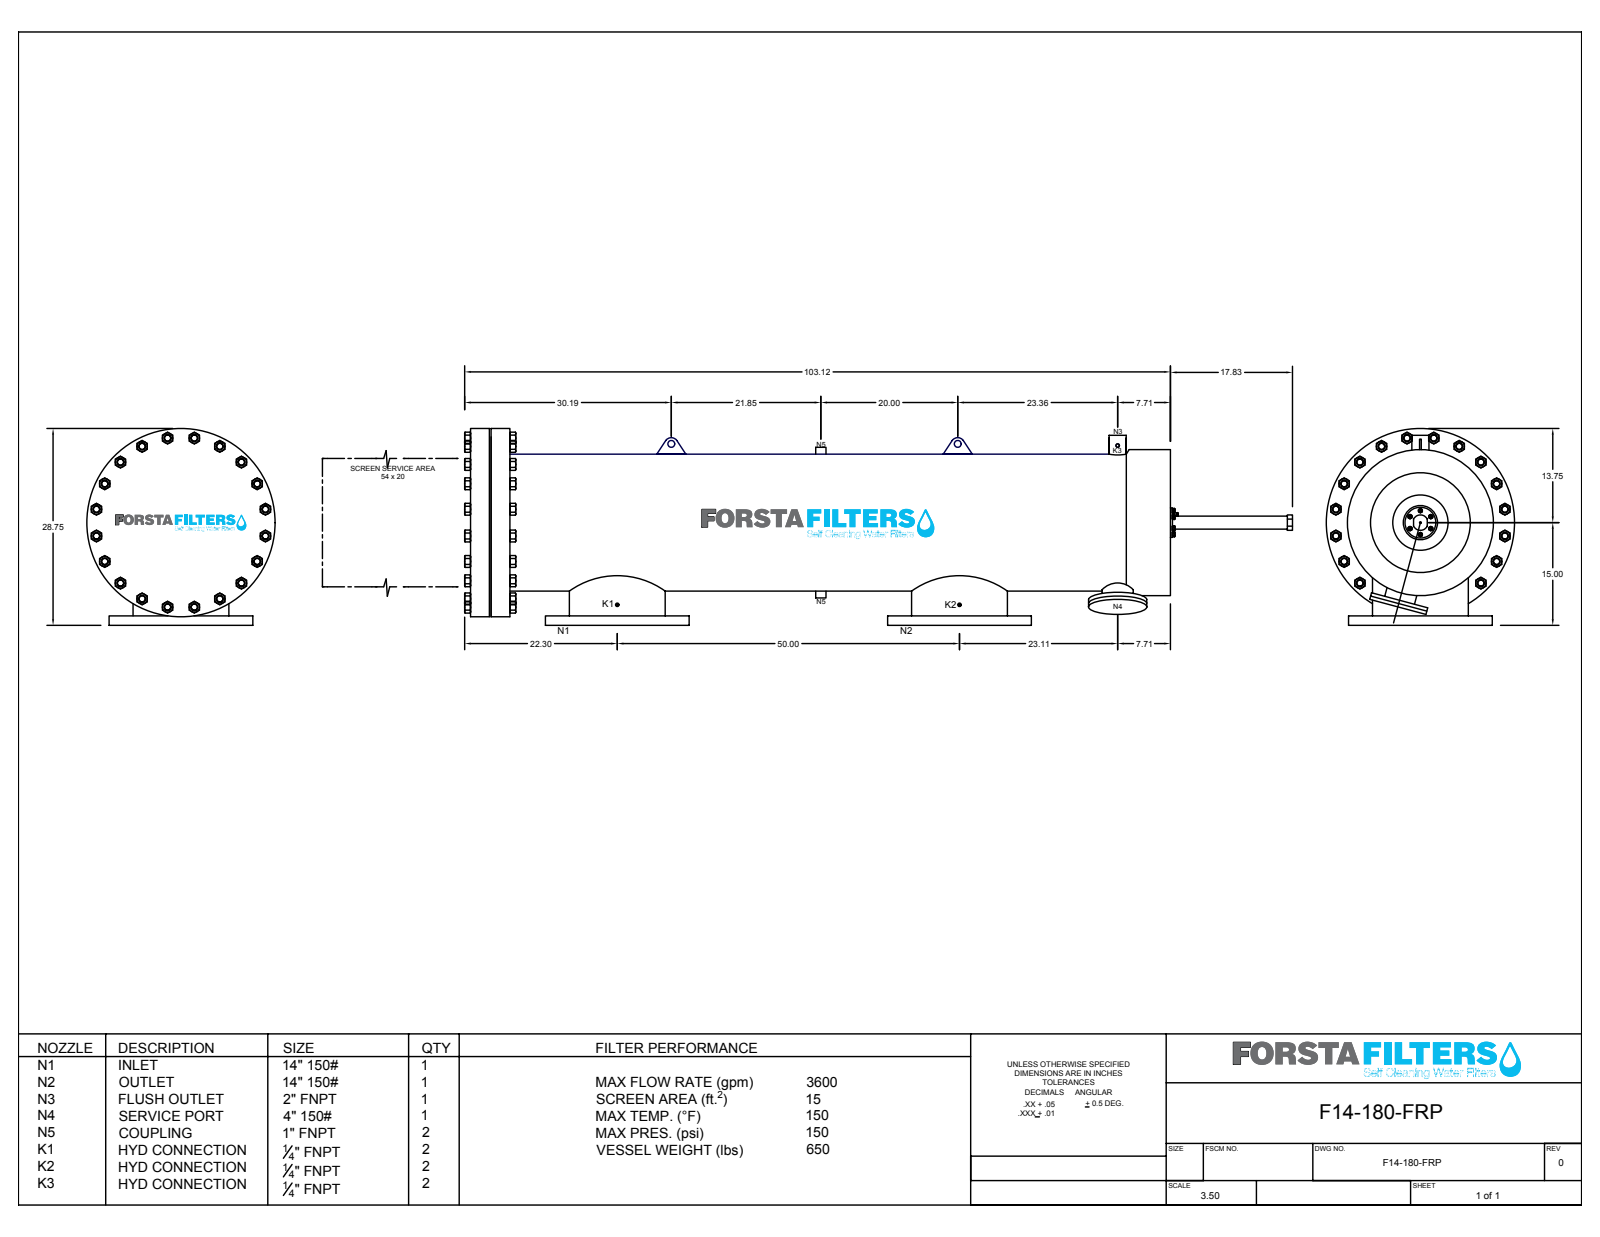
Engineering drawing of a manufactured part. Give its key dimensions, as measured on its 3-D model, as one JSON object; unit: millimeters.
{"part_name": "F14-FRP-180", "step_written_by": "SolidWorks 2018 (CONFIG_CONTROL_DESIGN)", "units": "millimeters", "bodies": {"solids": 23, "faces": 787, "planar": 372, "cylindrical": 402, "other": 13}, "overall_size": [2957.9, 730.2, 698.4], "volume_mm3": 73890000, "surface_area_mm2": 12150000, "round_holes": [[28.4, 24], [25.4, 19], [19.1, 16], [9.7, 6], [6.4, 3], [101.6, 2], [355.6, 2], [6.2, 1], [35.4, 1], [50.8, 1], [531.6, 1]], "round_bosses_or_shafts": [[9.5, 6], [533.4, 2], [365.6, 2], [228.6, 2], [111.6, 2], [16.4, 2], [698.4, 1], [541.7, 1]], "partial_cylinders_radius": [[25.4, 2]], "face_to_face_distances": [69.9, 76.2, 6.4, 2488, 2418.1, 2411.8, 35.1, 2483, 2413.1, 2406.8], "hole_center_spacings": [238.1, 123.3, 336.8, 412.4, 460, 134.7, 238.1, 317.5]}
